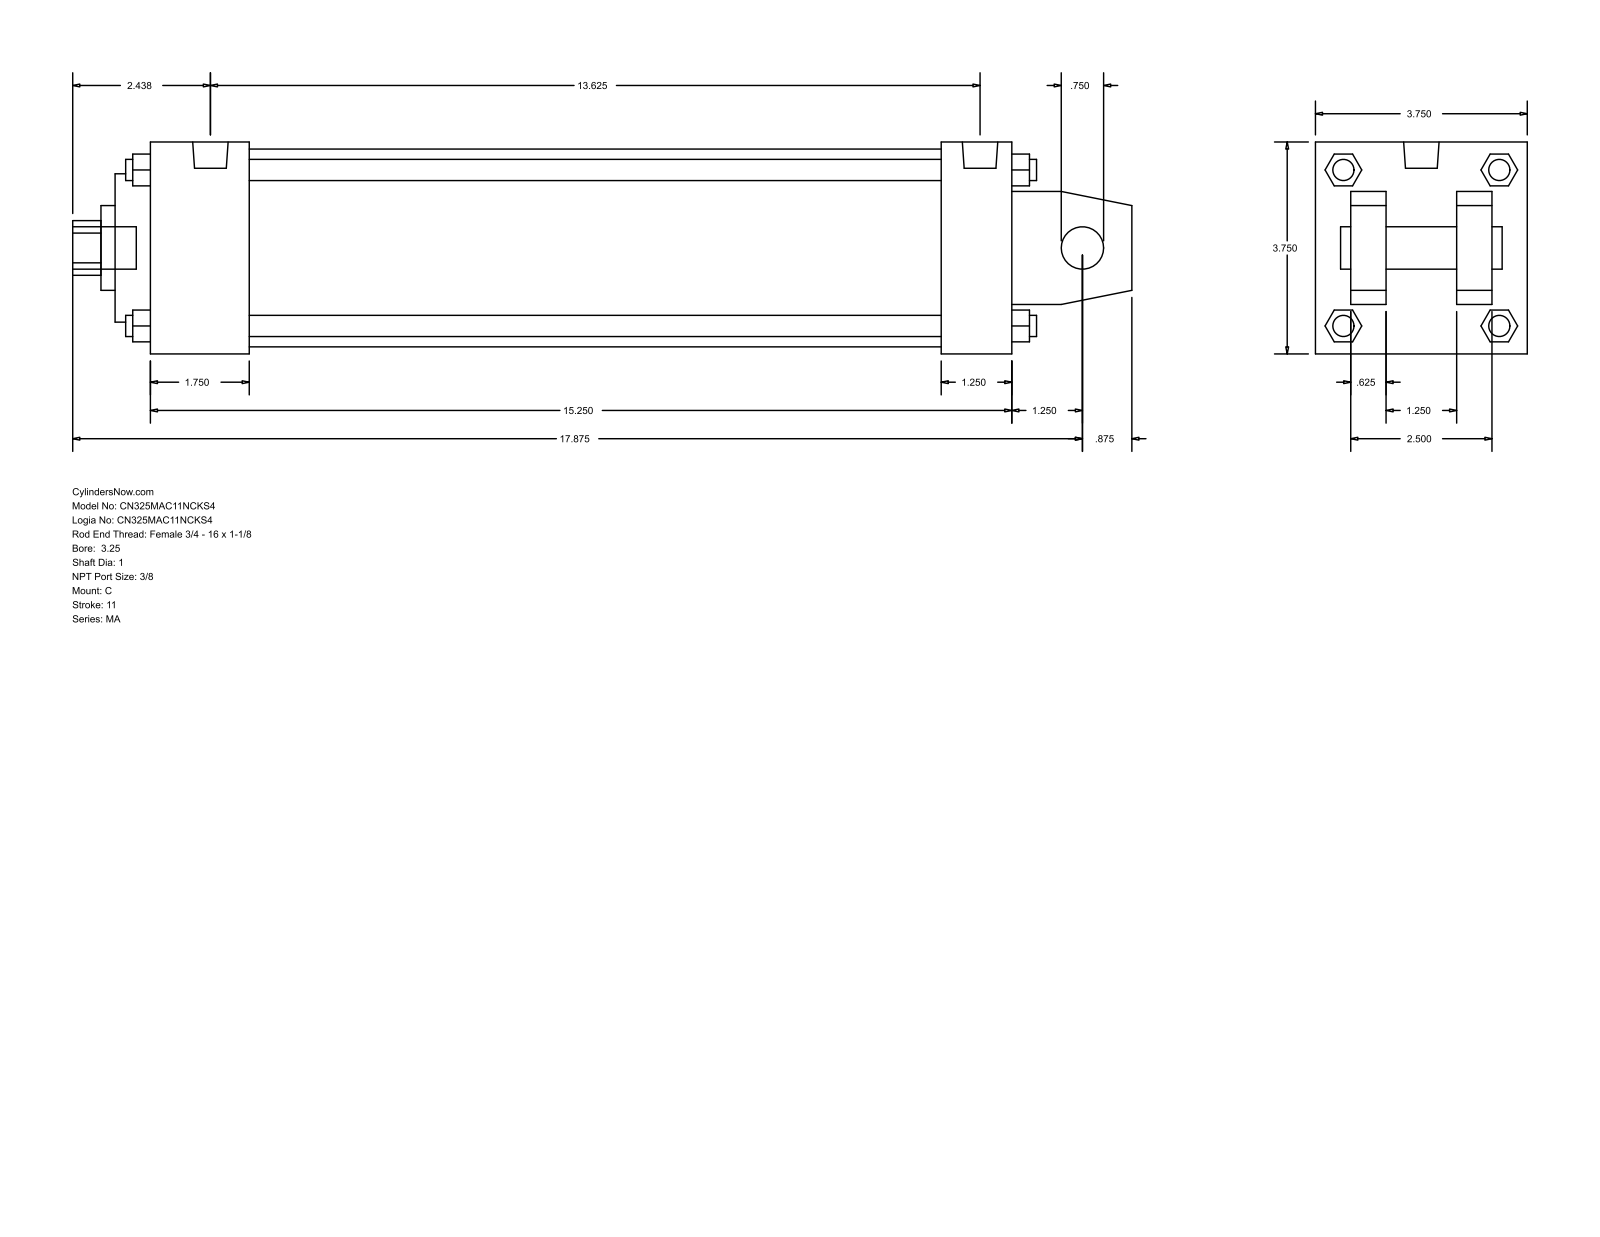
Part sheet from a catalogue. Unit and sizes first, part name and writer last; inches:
Units: inches
Overall size (bounding box): 18.75 × 3.75 × 3.75
Round holes (diameter × count): ⌀0.75 ×1, ⌀1 ×1, ⌀1.5 ×1, ⌀2.625 ×1, ⌀3.5 ×1
Round bosses / shafts (diameter × count): ⌀0.437 ×4, ⌀0.375 ×4, ⌀0.627 ×2, ⌀0.75 ×1
Partial cylindrical surfaces — rounded edges, fillets, slot ends (radius × count): R0.484 ×1
Main face-to-face distances: 3.75, 0.625, 2.5, 15.25, 1.25, 3.125, 1.875, 15.875, 14, 1.25
Bodies: 0 solids, 141 faces (109 planar, 32 cylindrical, 0 other)
Part name (STEP PRODUCT): MA_C__0325_1
STEP written by: GSSL Pune (CONFIG_CONTROL_DESIGN)
